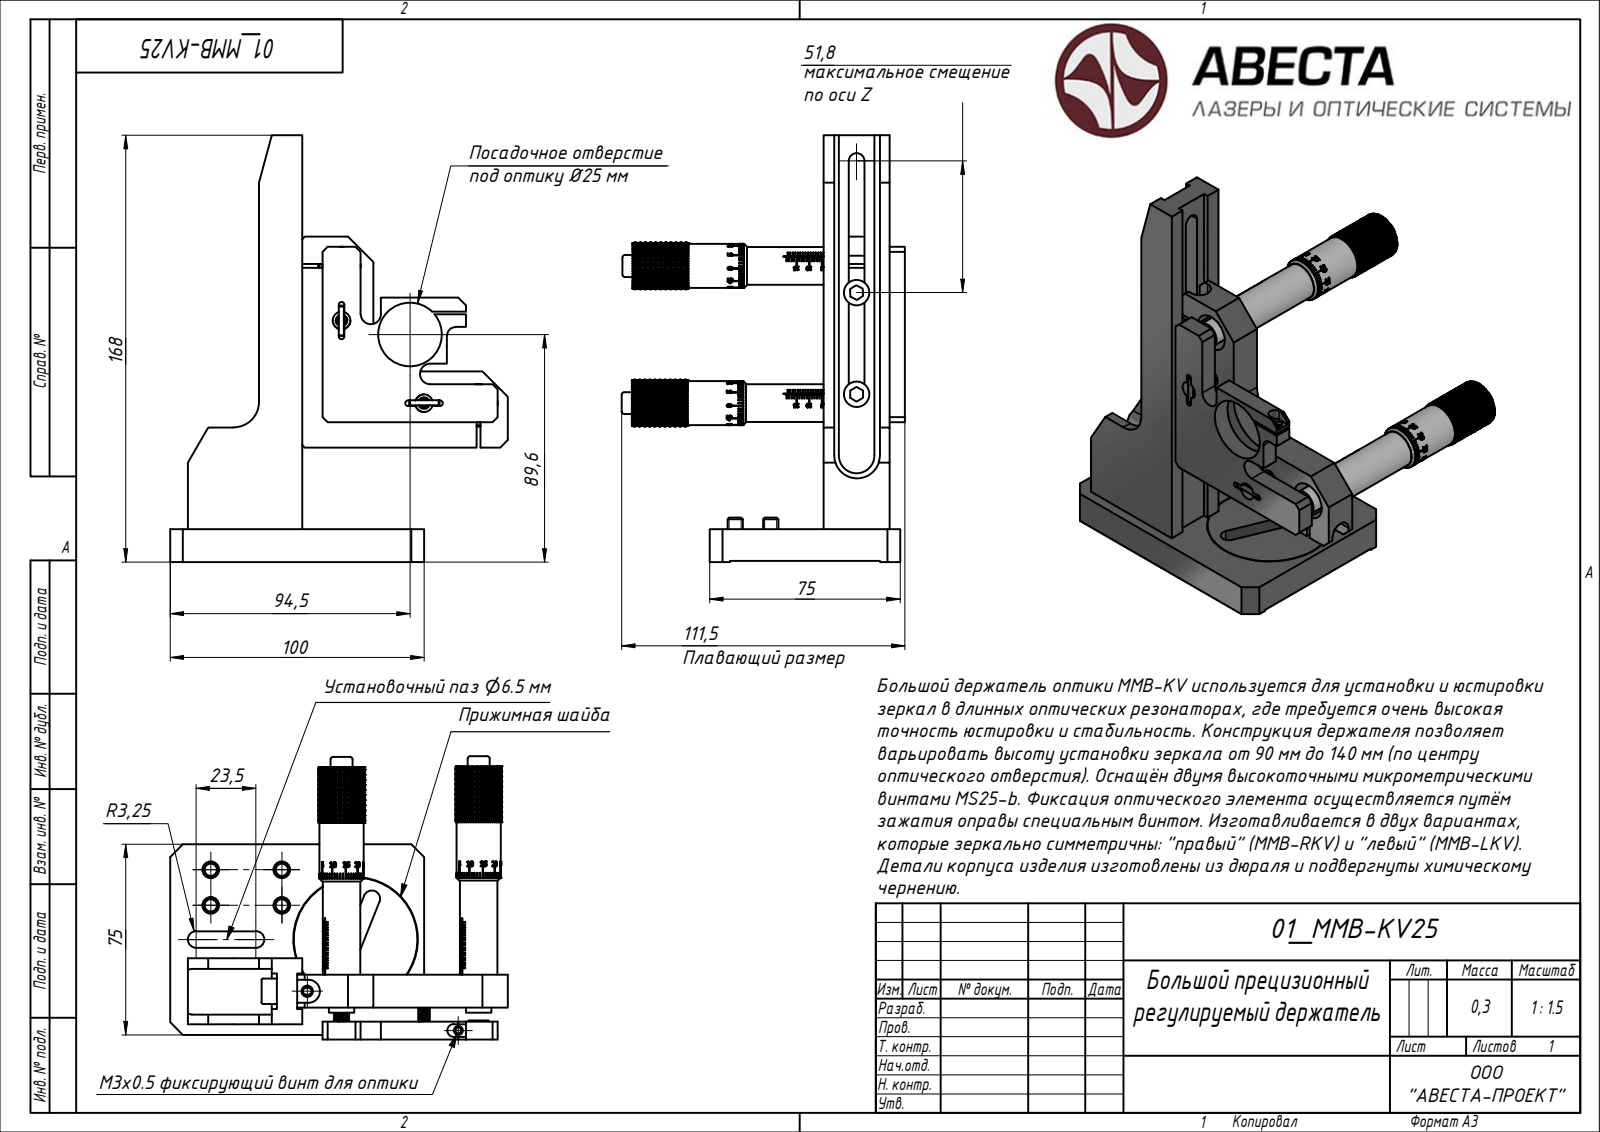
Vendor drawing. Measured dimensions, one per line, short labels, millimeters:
written by: ST-DEVELOPER v15 (AUTOMOTIVE_DESIGN)
unit: mm
bodies: 17 solids, 423 faces (179 planar, 0 cylindrical, 244 other)
size: 168 × 133 × 99.89
volume: 237 284 mm³; area: 82 420 mm²
face distances: 6.5, 19.5, 13, 10, 26, 7, 12.5, 20, 8, 0.5
